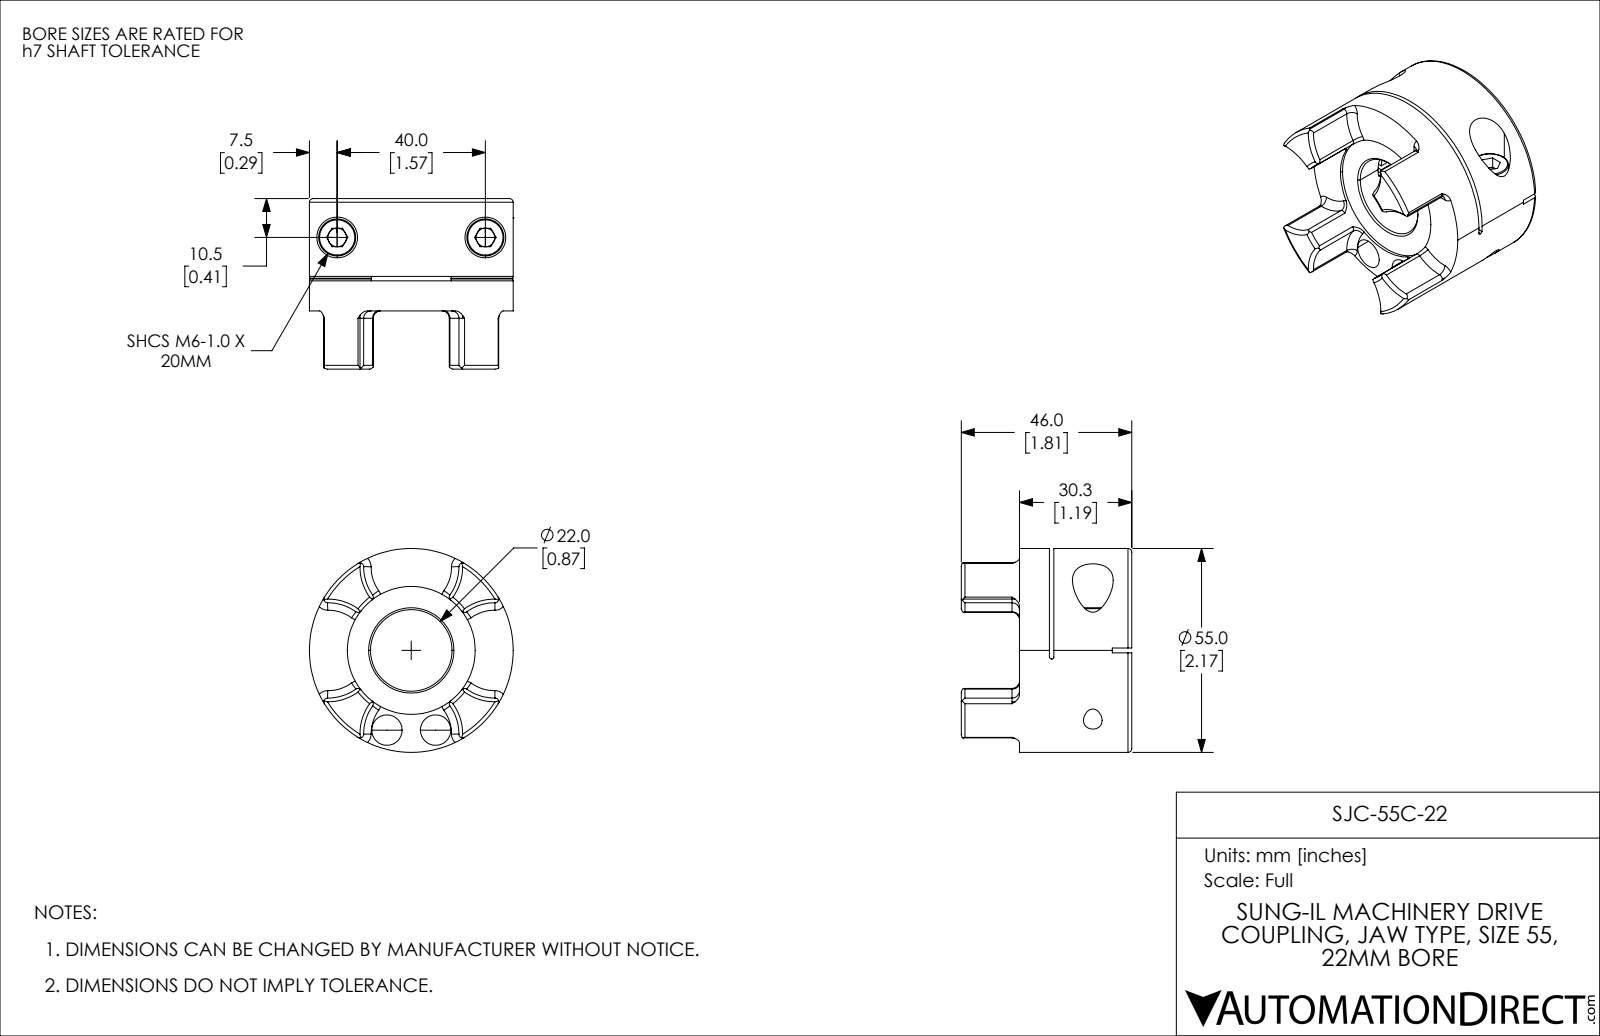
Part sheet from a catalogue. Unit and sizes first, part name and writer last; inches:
Units: inches
Overall size (bounding box): 2.165 × 2.165 × 1.811
Round holes (diameter × count): ⌀0.197 ×2, ⌀0.252 ×2, ⌀0.323 ×2, ⌀0.433 ×2, ⌀0.866 ×1, ⌀1.358 ×1
Round bosses / shafts (diameter × count): ⌀0.394 ×2, ⌀0.236 ×2, ⌀2.165 ×1
Partial cylindrical surfaces — rounded edges, fillets, slot ends (radius × count): R0.039 ×16, R0.506 ×4, R0.02 ×2, R1.969 ×1
Main face-to-face distances: 0.874, 0.047, 0.827, 0.319, 0.366, 1.193, 0.031, 0.287, 0.335, 1.161
Hole centre spacings: 0.885, 0.517, 1.575
Volume: 3.747 in³ · Surface area: 31.14 in²
Bodies: 3 solids, 206 faces (52 planar, 72 cylindrical, 82 other)
Part name (STEP PRODUCT): SJC-55C-22
STEP written by: SolidWorks 2021 (CONFIG_CONTROL_DESIGN)
